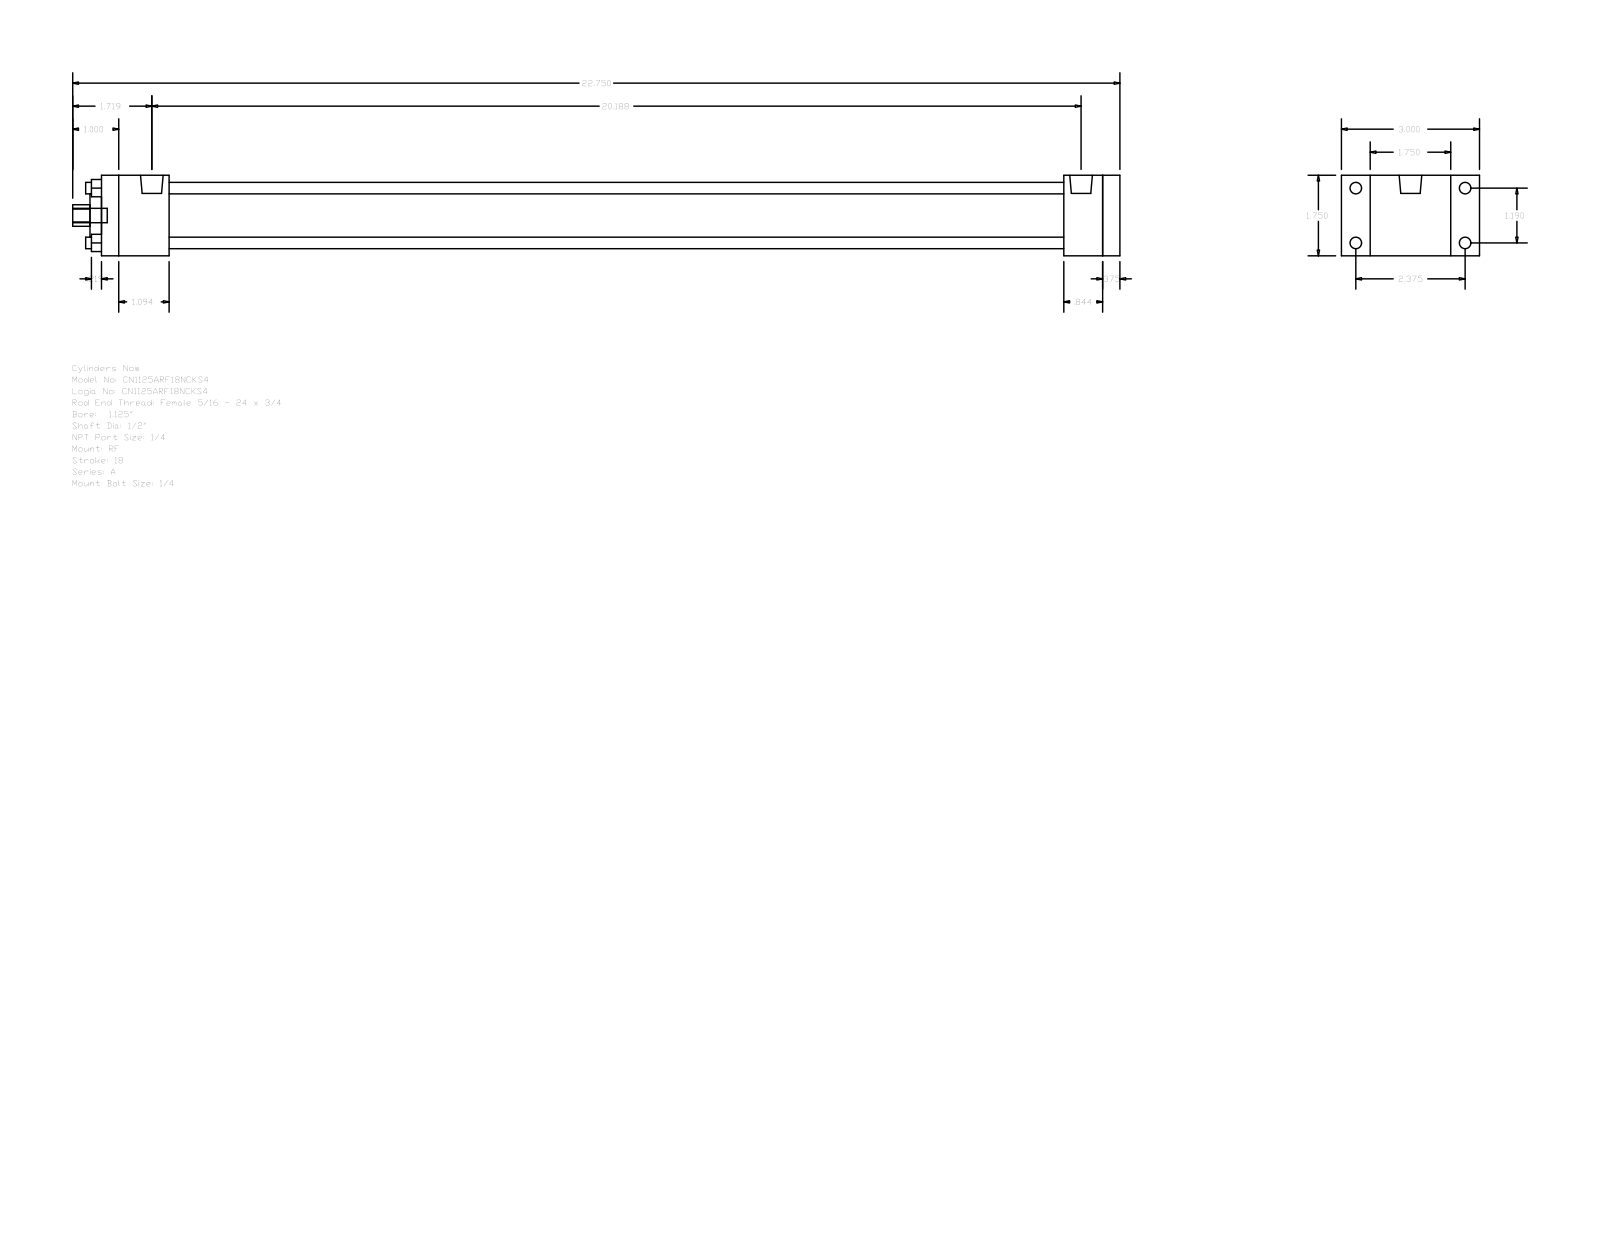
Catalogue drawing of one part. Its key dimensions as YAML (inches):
part_name: "A_RF__0112_0.5"
step_written_by: "GSSL Pune (CONFIG_CONTROL_DESIGN)"
units: inches
bodies: {solids: 0, faces: 92, planar: 64, cylindrical: 28, other: 0}
overall_size: [22.75, 3, 1.75]
round_holes:
  - {diameter: 0.25, count: 4}
  - {diameter: 0.5, count: 1}
  - {diameter: 0.937, count: 1}
  - {diameter: 1.255, count: 1}
round_bosses_or_shafts:
  - {diameter: 0.25, count: 4}
  - {diameter: 0.219, count: 4}
  - {diameter: 0.492, count: 2}
  - {diameter: 0.313, count: 1}
partial_cylinders:
  - {radius: 0.234, count: 1}
face_to_face_distances: [1.75, 0.375, 21.75, 22.125, 1.469, 20.906, 19.437, 20.281, 20.656, 0.844]
hole_center_spacings: [0.841, 1.19, 1.683]
